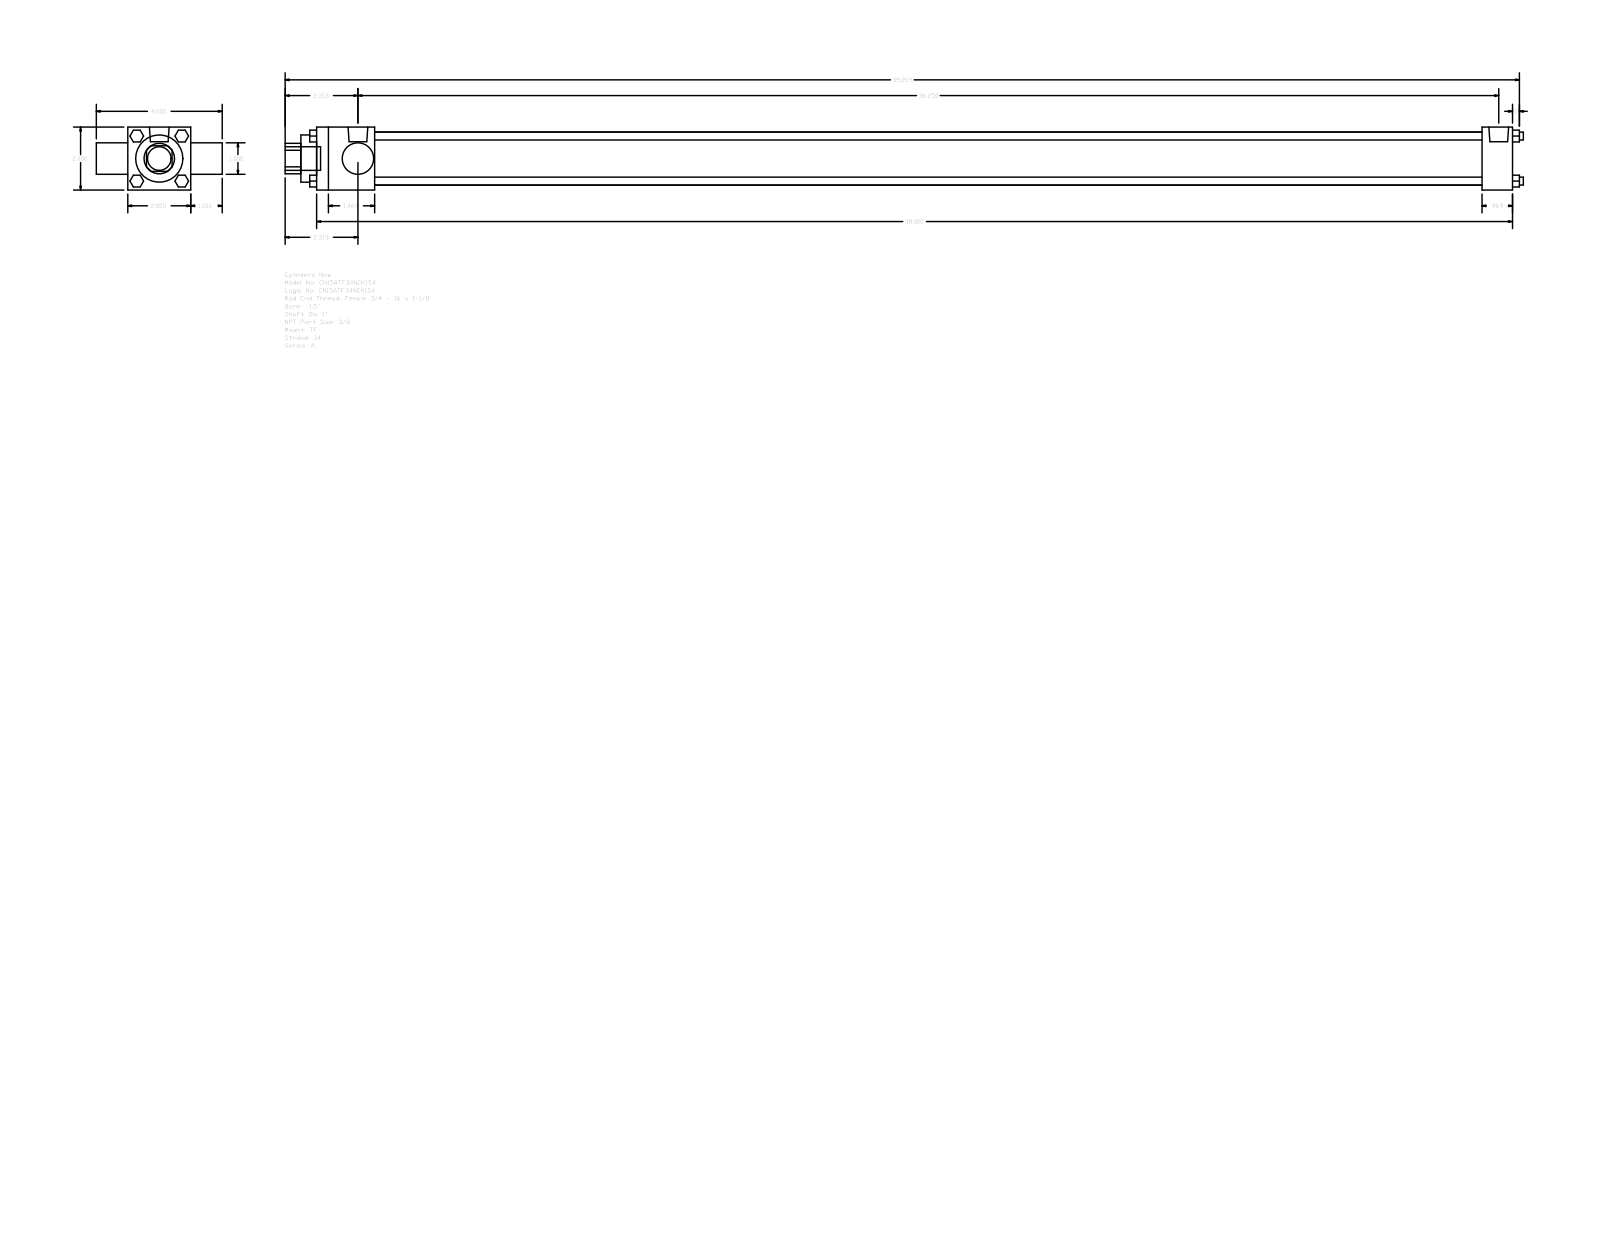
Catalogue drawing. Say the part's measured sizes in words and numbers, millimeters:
The part is named "A_TF__0150_1". Its 3-D file was written by "GSSL Pune (CONFIG_CONTROL_DESIGN)". It is 0 solids with 120 faces: 92 planar, 28 cylindrical and 0 other. Overall it measures 999.33 by 101.6 by 50.8 millimeters. Round holes: 2 of diameter 25.4, 1 of diameter 38.1, 1 of diameter 42.93. Round bosses or shafts: 4 of diameter 6.35, 3 of diameter 5.56, 2 of diameter 15.93, 1 of diameter 19.05. Partial cylindrical surfaces (rounded edges, fillets, slot ends): 1 of radius 12.29. The main face-to-face distances are 50.8, 25.4, 965.2, 76.2, 46.83, 940.59, 893.76, 918.37, 24.61, 12.7.
